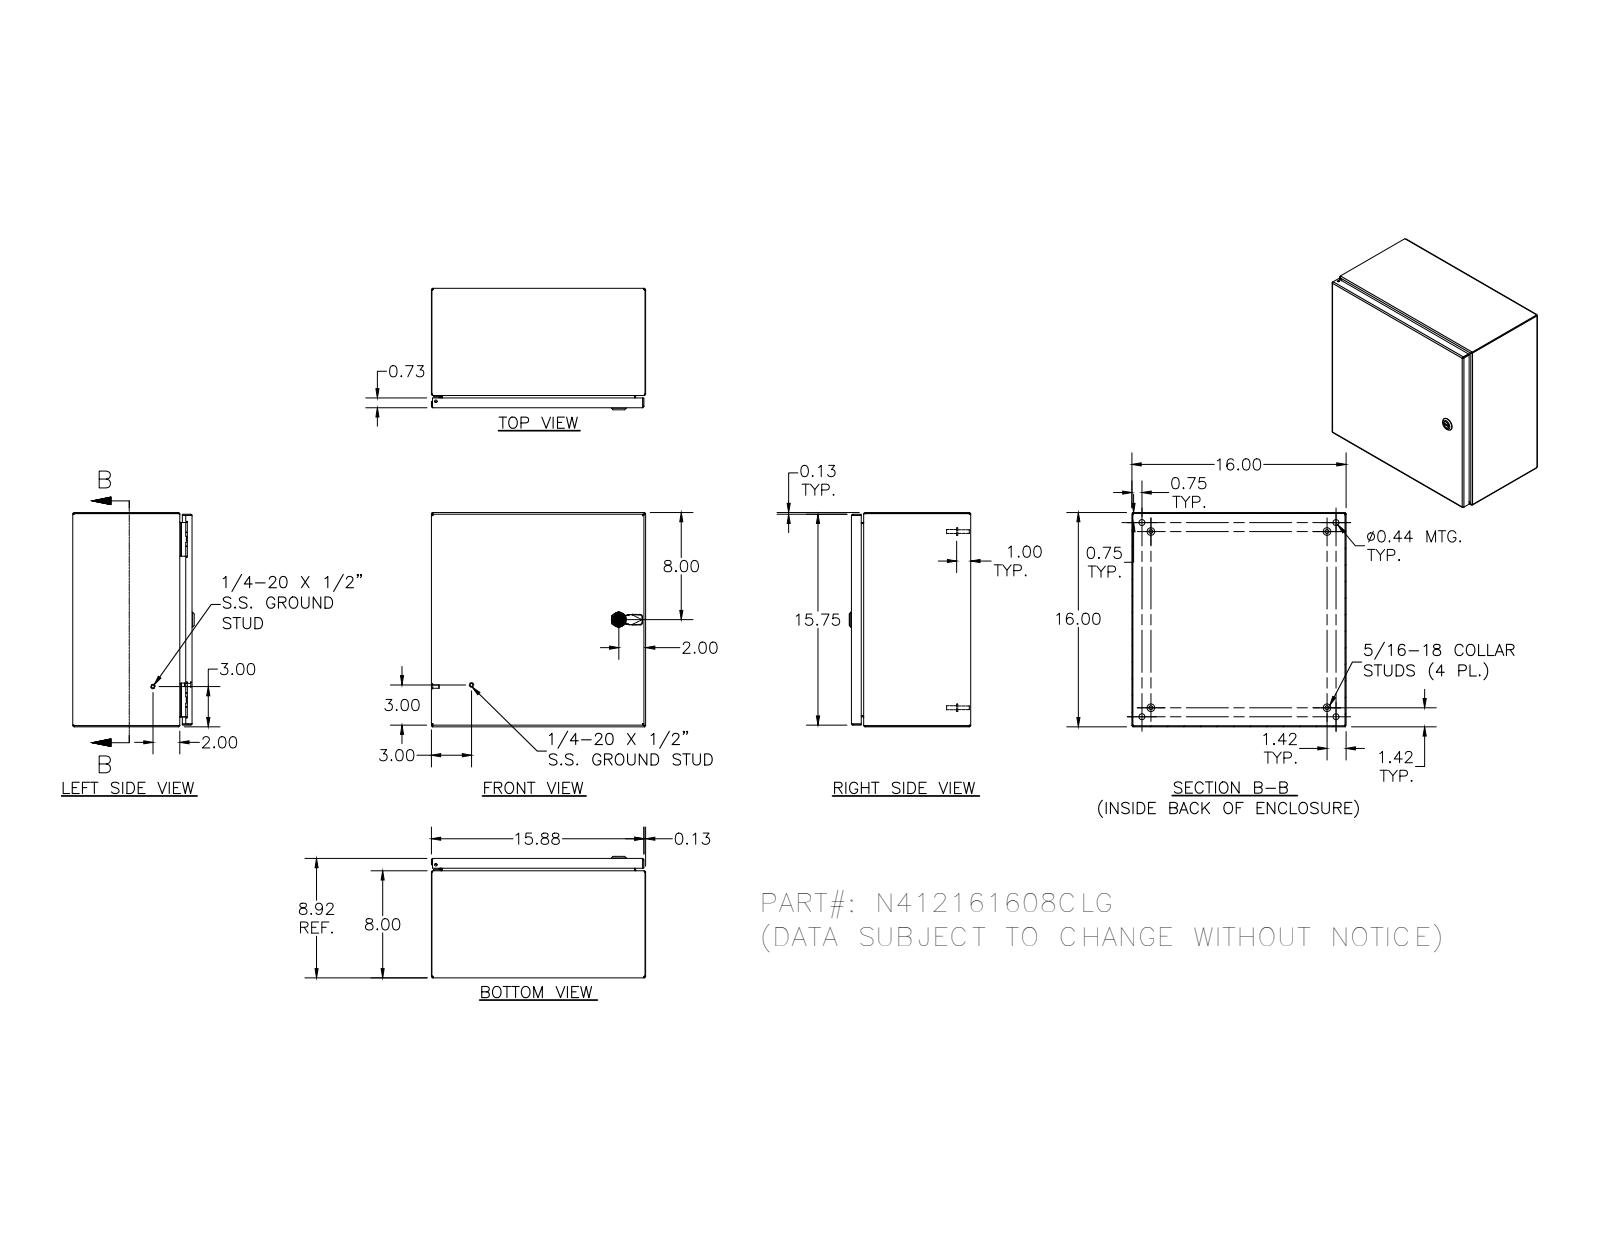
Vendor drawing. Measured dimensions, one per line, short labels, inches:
name: N412161608CLG
written by: SolidWorks 2018 (AUTOMOTIVE_DESIGN)
unit: in
bodies: 33 solids, 1449 faces (530 planar, 547 cylindrical, 372 other)
size: 16 × 16 × 9.075
volume: 85.74 in³; area: 2 334 in²
holes: 5× ⌀0.188, 4× ⌀0.093, 4× ⌀0.152, 4× ⌀0.167, 4× ⌀0.172, 4× ⌀0.437, 2× ⌀0.156, 1× ⌀0.187, 1× ⌀0.197, 1× ⌀0.315, 1× ⌀0.394, 1× ⌀0.402
bosses: 10× ⌀0.25, 5× ⌀0.131, 4× ⌀0.563, 4× ⌀0.36, 4× ⌀0.32, 4× ⌀0.3, 4× ⌀0.275, 4× ⌀0.256
rounds: 30× R0.012, 30× R0.031, 26× R0.05, 20× R0.105, 18× R0.016, 16× R0.125, 13× R0.02, 8× R0.032
face distances: 0.074, 8.843, 15.926, 15.852, 0.074, 15.926, 16, 8.769, 8.917, 0.917
hole spacings: 12, 0.66, 0.656, 1.307, 1.965, 11.34, 12.66, 14.5
